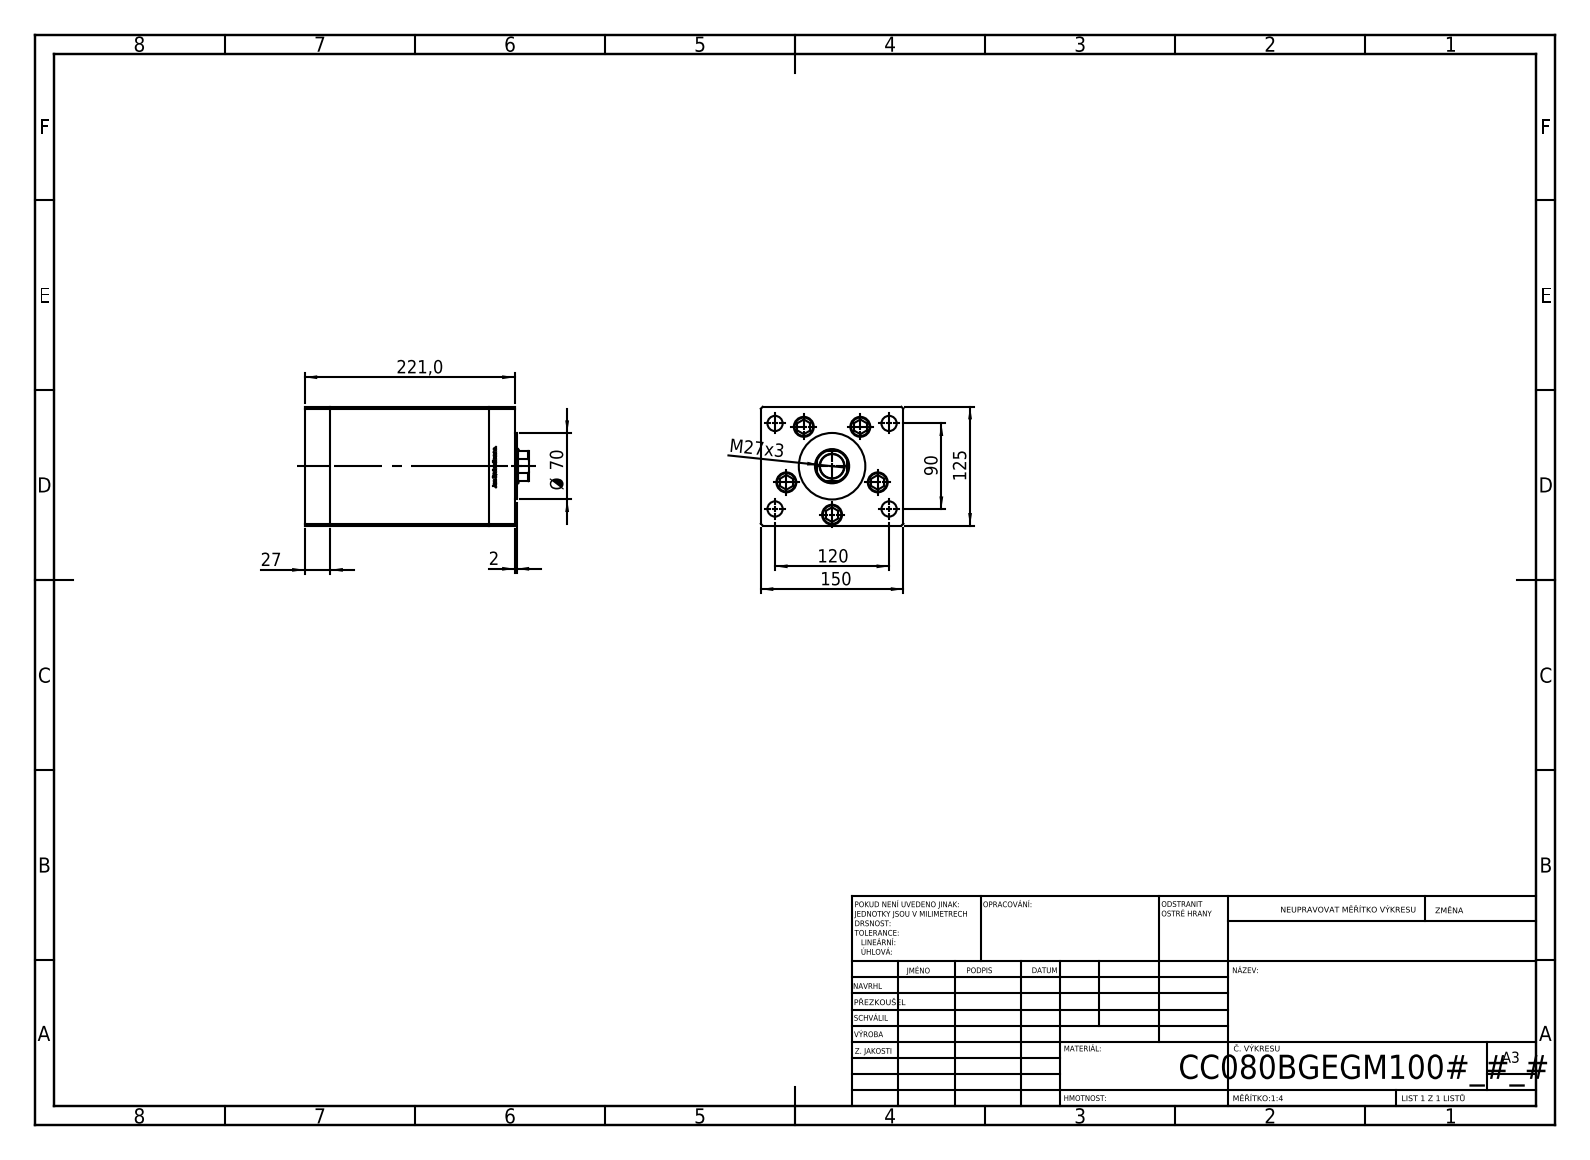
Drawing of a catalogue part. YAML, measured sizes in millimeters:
part_name: "V220C_FRONT_B; V220C BACK_B; V220C_VC_B; ALLEN BOLT (+1 more)"
step_written_by: "SolidWorks 2019 (CONFIG_CONTROL_DESIGN)"
units: millimeters
bodies: {solids: 14, faces: 1185, planar: 464, cylindrical: 147, other: 574}
overall_size: [236, 150, 125]
volume: 3580000
surface_area: 367811
round_holes:
  - {diameter: 17.5, count: 5}
  - {diameter: 21, count: 5}
  - {diameter: 16, count: 4}
  - {diameter: 2, count: 2}
  - {diameter: 13.16, count: 2}
  - {diameter: 25.5, count: 1}
  - {diameter: 36, count: 1}
round_bosses_or_shafts:
  - {diameter: 8, count: 5}
  - {diameter: 80, count: 1}
  - {diameter: 70, count: 1}
partial_cylinders:
  - {radius: 0.93, count: 2}
  - {radius: 17.5, count: 1}
face_to_face_distances: [27, 194, 125, 167, 150, 33.5, 221, 6.5, 160.5, 187.5]
hole_center_spacings: [51, 75, 30.43, 30.48, 58.89, 60.3, 61.25, 63.14]
